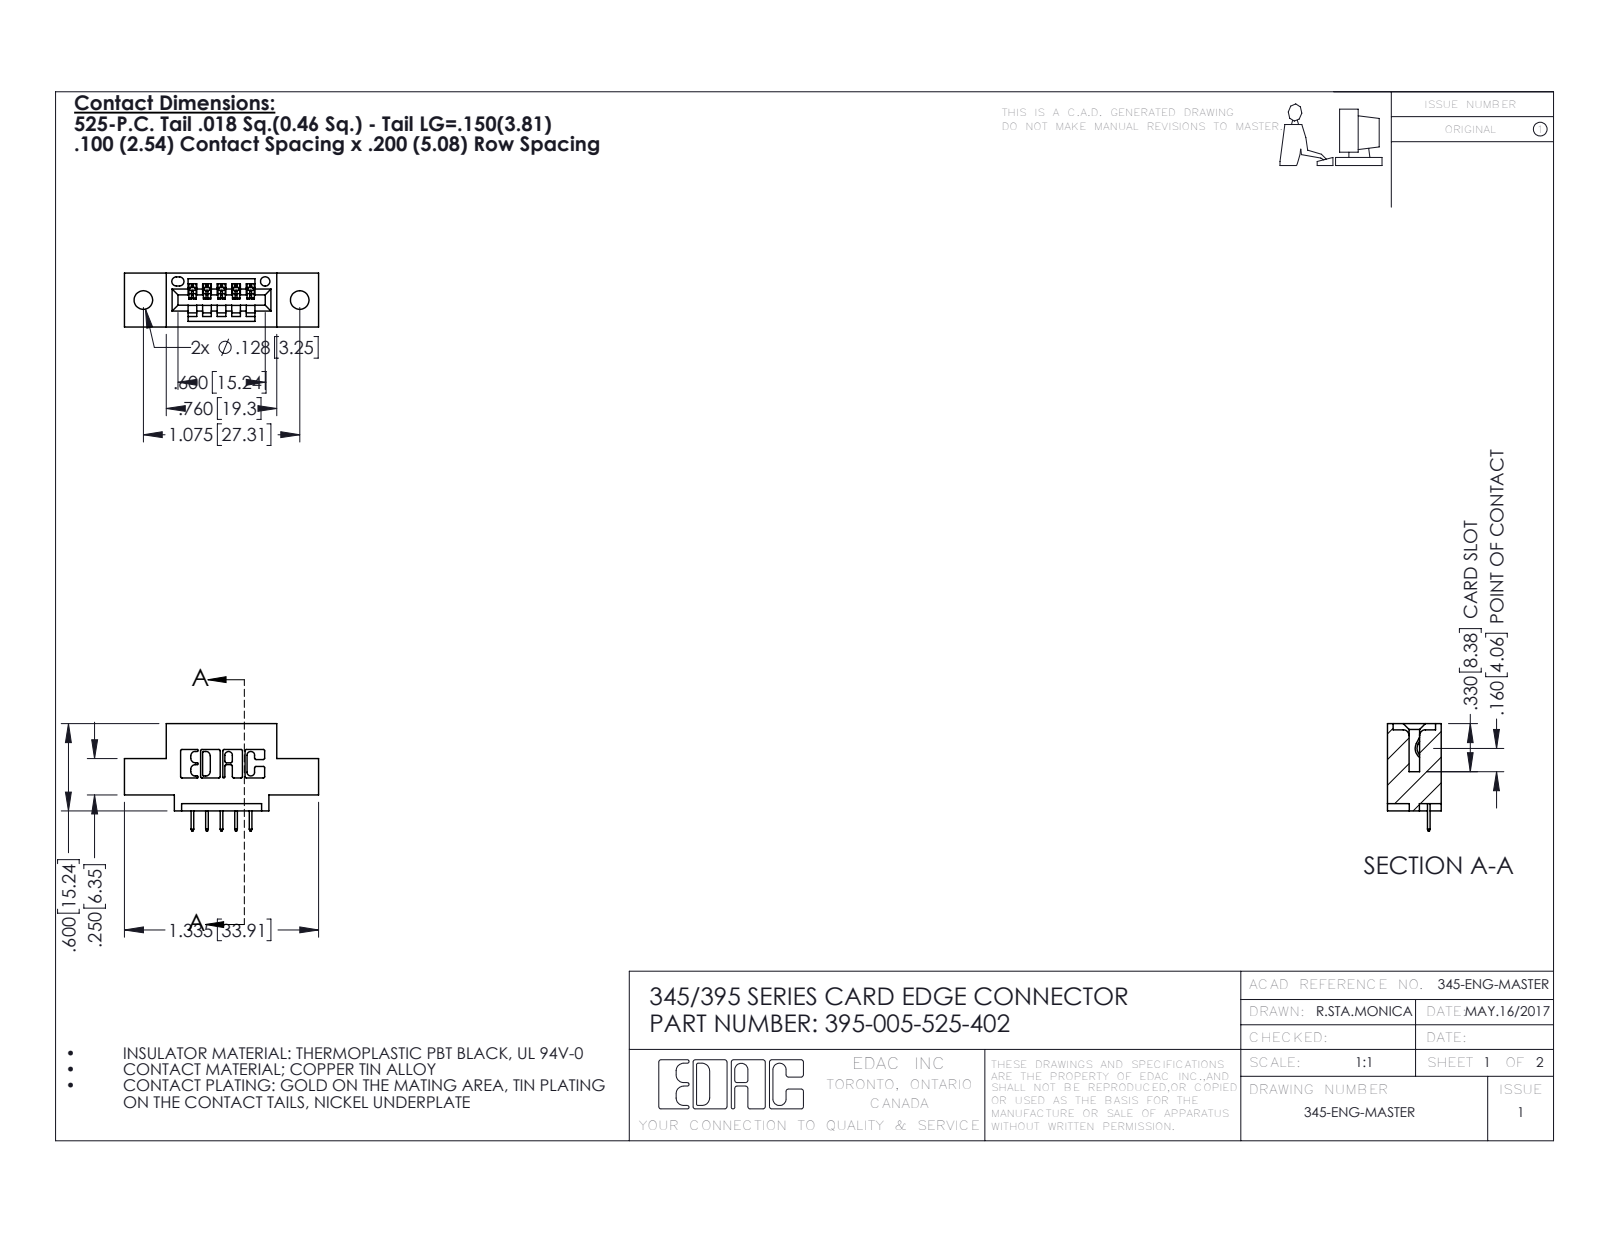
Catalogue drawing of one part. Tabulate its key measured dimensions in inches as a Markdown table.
| quantity | value |
| --- | --- |
| part name | 345 Part_0.110 Offset - 0.128 Dia; 395-005-525-402; 345-292-001_345-293-125 |
| STEP written by | SolidWorks 2020 (CONFIG_CONTROL_DESIGN) |
| units | inches |
| bodies | 6 solids, 440 faces (314 planar, 126 cylindrical, 0 other) |
| overall size | 1.335 × 0.737 × 0.37 |
| volume | 0.17 in³ |
| surface area | 4.562 in² |
| round holes (diameter × count) | 0.128 × 2, 0.064 × 1 |
| partial cylindrical surfaces (radius × count) | 0.01 × 22, 0.006 × 10, 0.007 × 6, 0.031 × 6, 0.026 × 3, 0.031 × 2, 0.04 × 2, 0.014 × 1 |
| main face-to-face distances | 0.37, 0.2, 0.1, 0.072, 0.298, 0.25, 0.025, 0.06, 0.16, 0.55 |
| hole center spacings | 0.27, 0.847, 1.075 |
